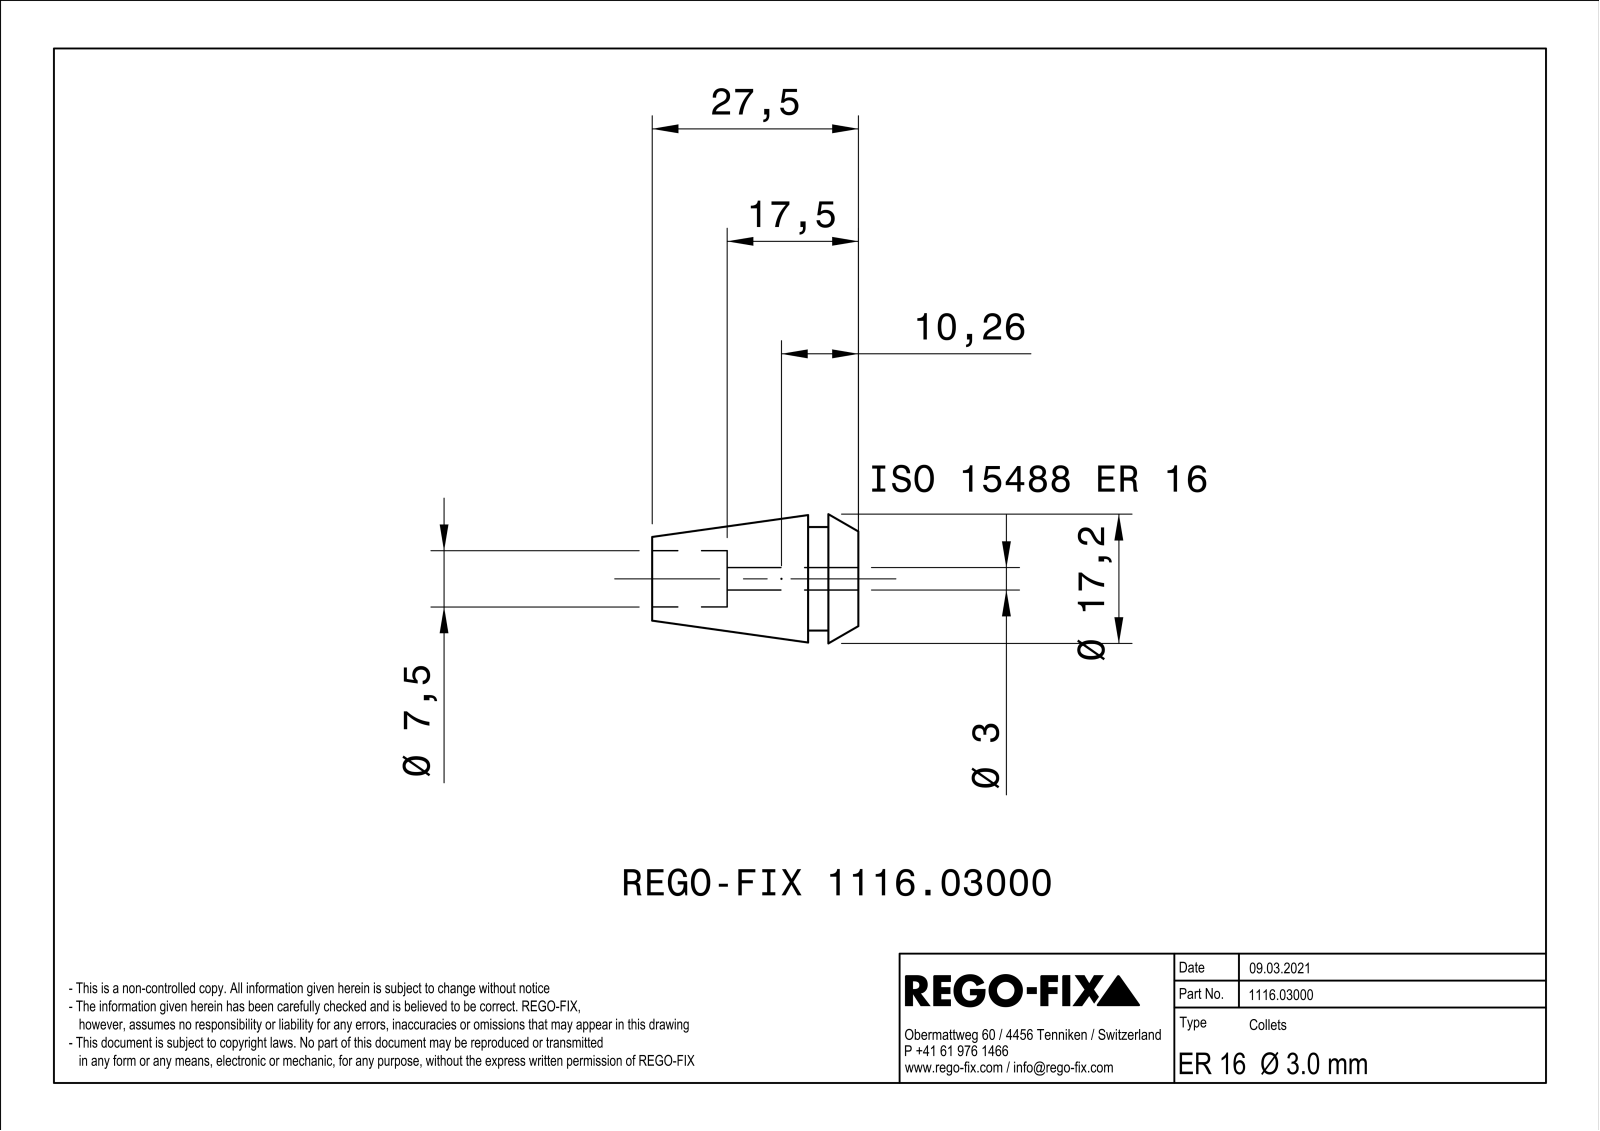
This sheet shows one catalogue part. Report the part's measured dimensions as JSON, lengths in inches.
{"part_name": "NOCUT", "step_written_by": "SIEMENS PLM Software Solid Edge ST10 (AUTOMOTIVE_DESIGN)", "units": "inches", "bodies": {"solids": 1, "faces": 240, "planar": 112, "cylindrical": 32, "other": 96}, "overall_size": [1.083, 0.679, 0.679], "volume_in3": 0.171, "surface_area_in2": 7.849, "round_holes": [[0.295, 1]], "partial_cylinders_radius": [[0.059, 1], [0.272, 1]], "face_to_face_distances": [0.024, 0.126, 0.15, 0.157, 0.264, 0.106, 0.276, 1.083, 0.925, 0.819]}
